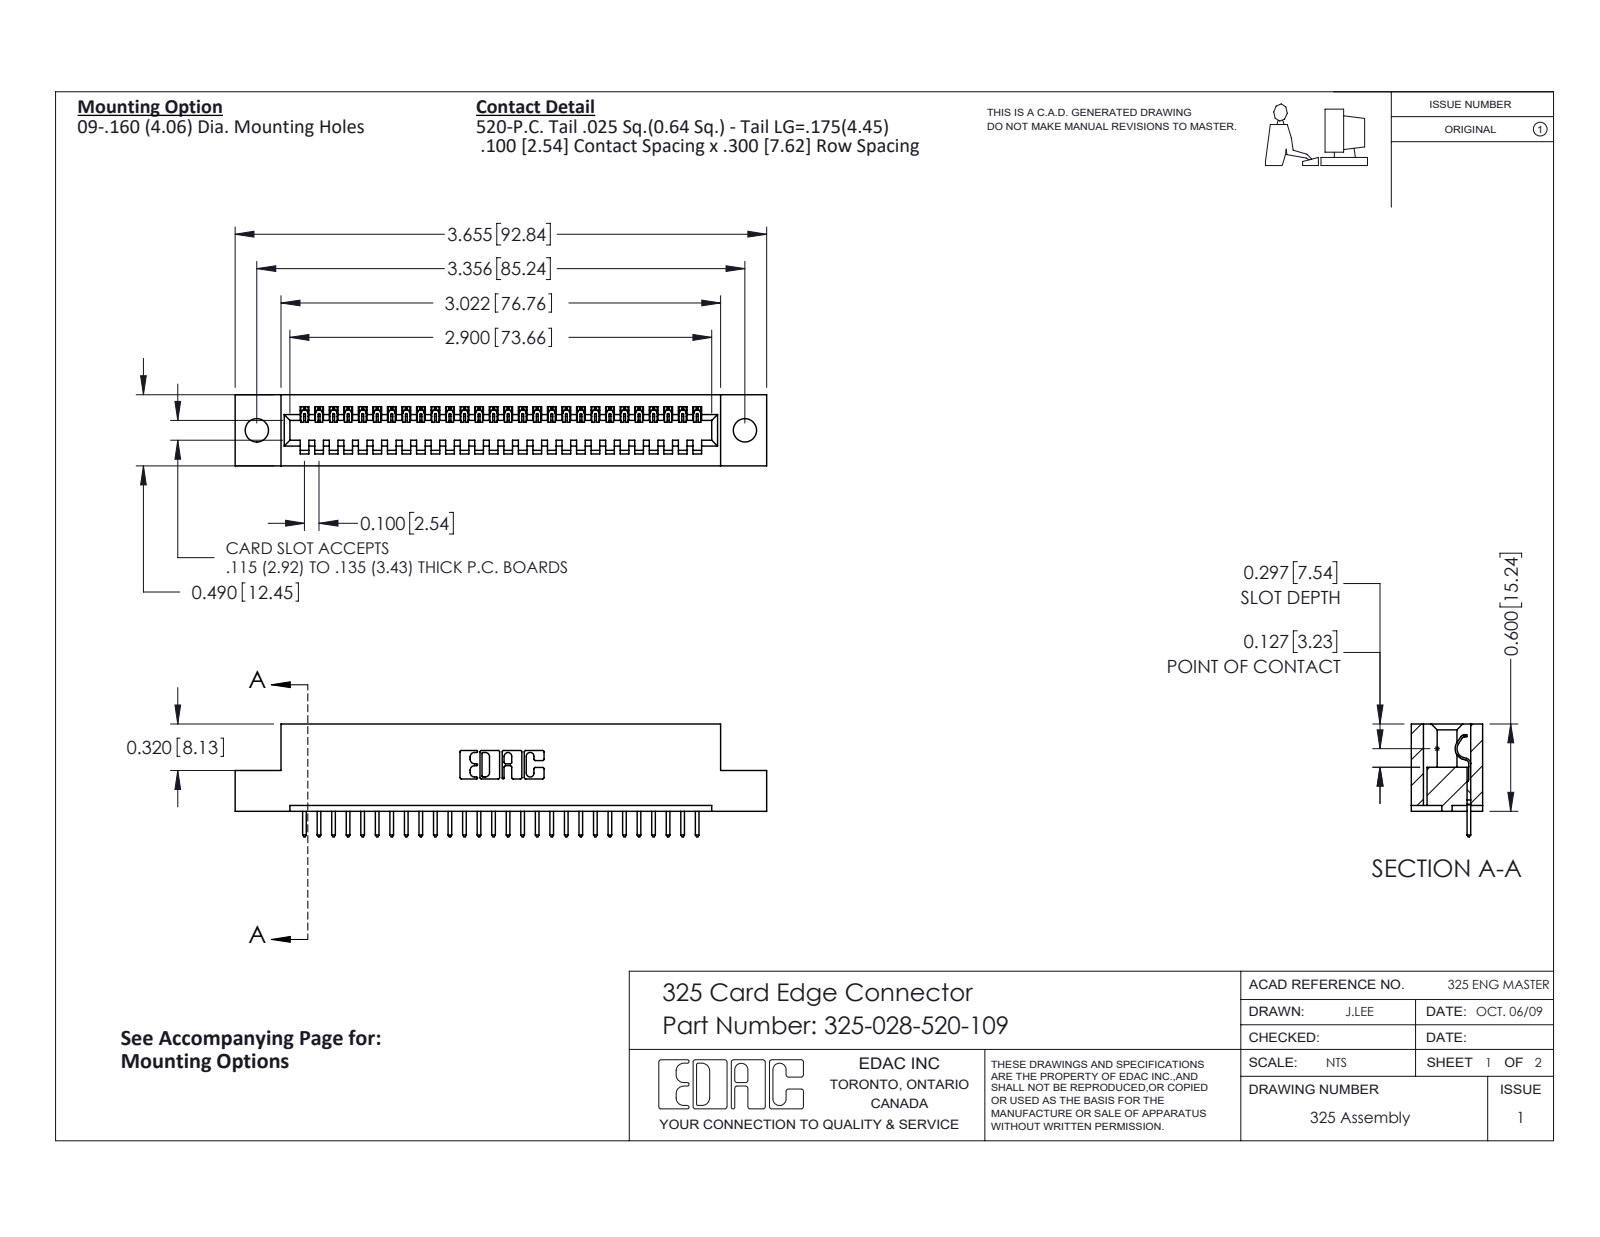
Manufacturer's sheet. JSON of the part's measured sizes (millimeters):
{"part_name": "325-292-001_325-293-120; 325-028-520-109; 325 Part_.160 TH", "step_written_by": "SolidWorks 2016 (CONFIG_CONTROL_DESIGN)", "units": "millimeters", "bodies": {"solids": 29, "faces": 1738, "planar": 1246, "cylindrical": 492, "other": 0}, "overall_size": [92.8, 19.7, 12.4], "volume_mm3": 11400, "surface_area_mm2": 11790, "round_holes": [[4.1, 2]], "partial_cylinders_radius": [[0.2, 56], [0.3, 56], [0.3, 22], [0.2, 6], [0.8, 6], [0.7, 3], [0.4, 1], [0.6, 1]], "face_to_face_distances": [2.1, 10.3, 12.4, 7.6, 2.7, 9.7, 0.6, 8.3, 1, 15.2], "hole_center_spacings": [85.2]}
